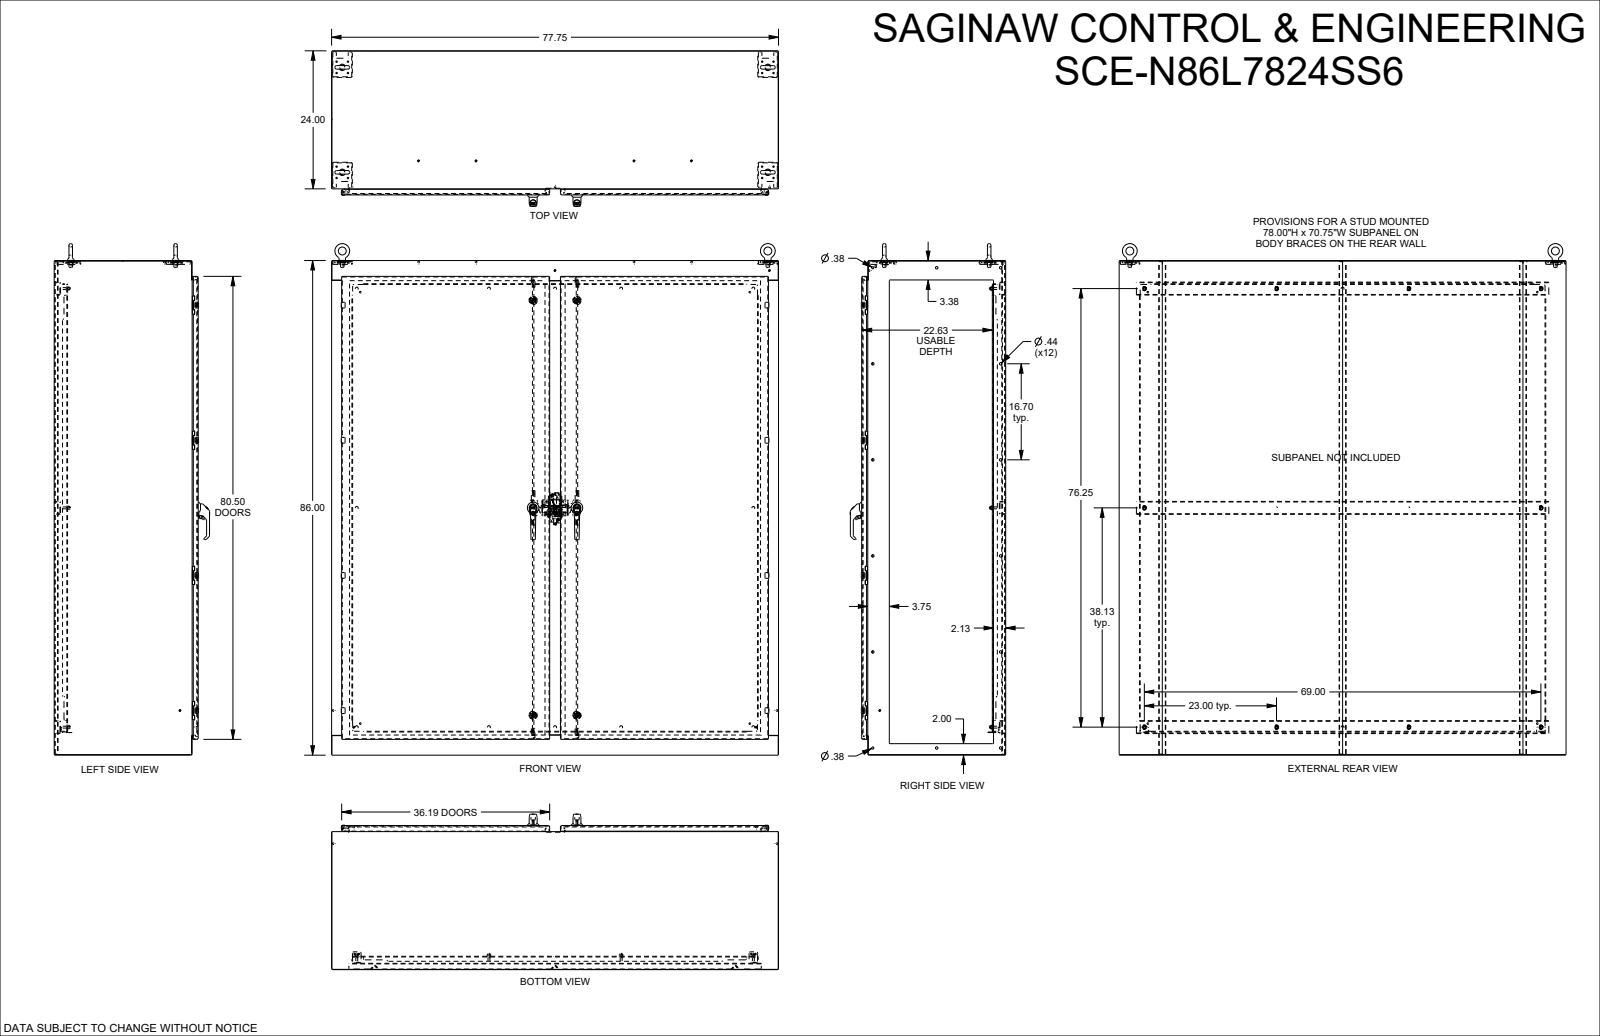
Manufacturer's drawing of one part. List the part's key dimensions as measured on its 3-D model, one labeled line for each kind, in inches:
Part name (STEP PRODUCT): SCE-N86L7824
STEP written by: SolidWorks 2023 (AUTOMOTIVE_DESIGN)
Units: inches
Bodies: 48 solids, 7310 faces (3016 planar, 2462 cylindrical, 1832 other)
Overall size (bounding box): 88.945 × 77.75 × 27.046
Volume: 2 387 in³ · Surface area: 45 388 in²
Round holes (diameter × count): ⌀0.25 ×20, ⌀0.375 ×18, ⌀0.205 ×16, ⌀0.244 ×16, ⌀0.437 ×12, ⌀0.04 ×8, ⌀0.17 ×8, ⌀0.218 ×8, ⌀0.256 ×4, ⌀0.343 ×4, ⌀0.344 ×4, ⌀0.36 ×4
Round bosses / shafts (diameter × count): ⌀0.17 ×24, ⌀0.25 ×20, ⌀0.24 ×16, ⌀0.196 ×10, ⌀1.4 ×4, ⌀1.173 ×4, ⌀0.6 ×4, ⌀0.341 ×4
Partial cylindrical surfaces — rounded edges, fillets, slot ends (radius × count): R0.03 ×196, R0.015 ×166, R0.125 ×100, R0.02 ×74, R0.02 ×48, R0.25 ×44, R0.039 ×42, R0.04 ×40
Main face-to-face distances: 0.104, 24.954, 25.058, 24.85, 85.896, 23.896, 1.058, 86, 85.792, 23.792
Hole centre spacings: 1.979, 23.5, 16.7, 27.82, 1.4, 33.4, 40.133, 47
